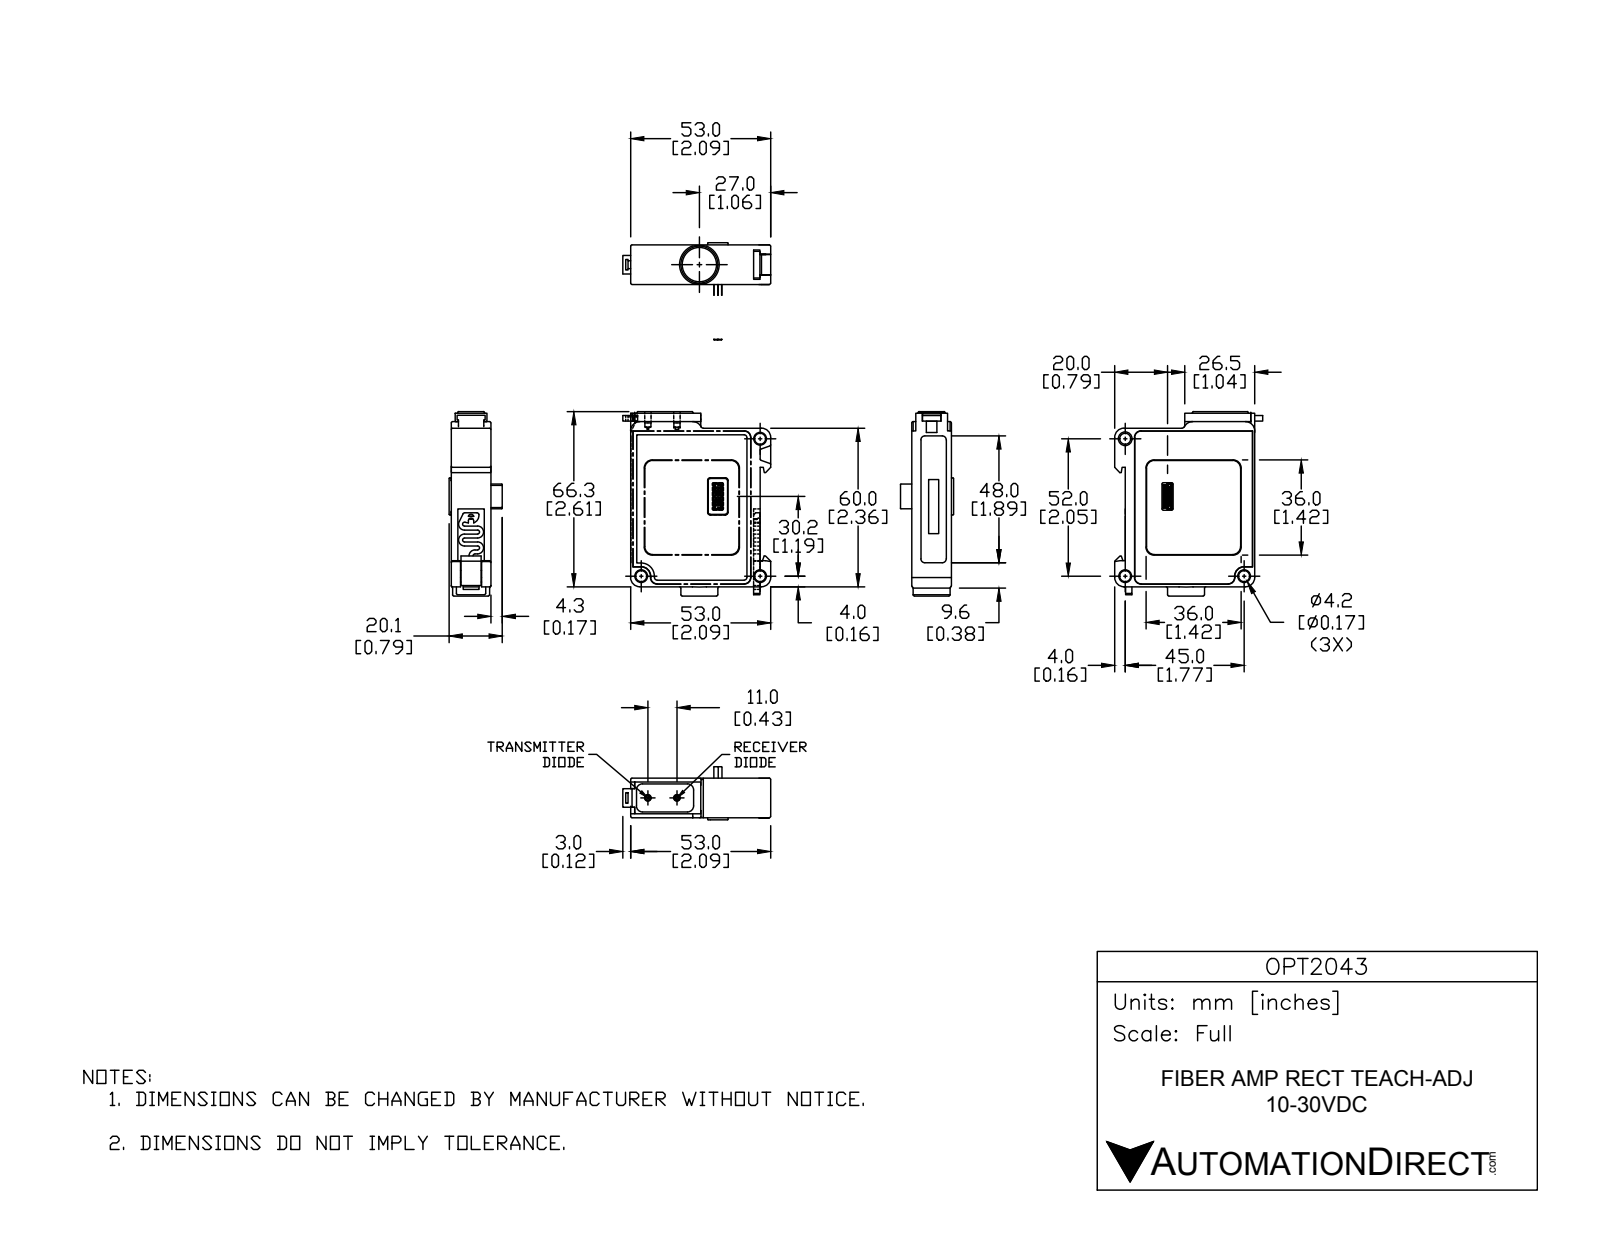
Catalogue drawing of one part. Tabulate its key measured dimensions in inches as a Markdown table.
| quantity | value |
| --- | --- |
| part name | OPT2043 |
| STEP written by | SolidWorks 2014 (AUTOMOTIVE_DESIGN) |
| units | inches |
| bodies | 1 solid, 941 faces (445 planar, 311 cylindrical, 185 other) |
| overall size | 2.748 × 2.205 × 0.791 |
| volume | 2.849 in³ |
| surface area | 19.38 in² |
| round holes (diameter × count) | 0.165 × 3, 0.071 × 2, 0.091 × 2, 0.094 × 2, 0.047 × 1, 0.173 × 1 |
| round bosses / shafts (diameter × count) | 0.02 × 12, 0.551 × 1 |
| partial cylindrical surfaces (radius × count) | 0.008 × 60, 0.02 × 32, 0.004 × 15, 0.006 × 15, 0.039 × 14, 0.016 × 12, 0.03 × 9, 0.118 × 9 |
| main face-to-face distances | 0.586, 0.582, 0.59, 1.925, 0.591, 0.587, 1.929, 0.098, 2.362, 0.059 |
| hole center spacings | 0.433, 1.772, 2.047, 2.707 |
